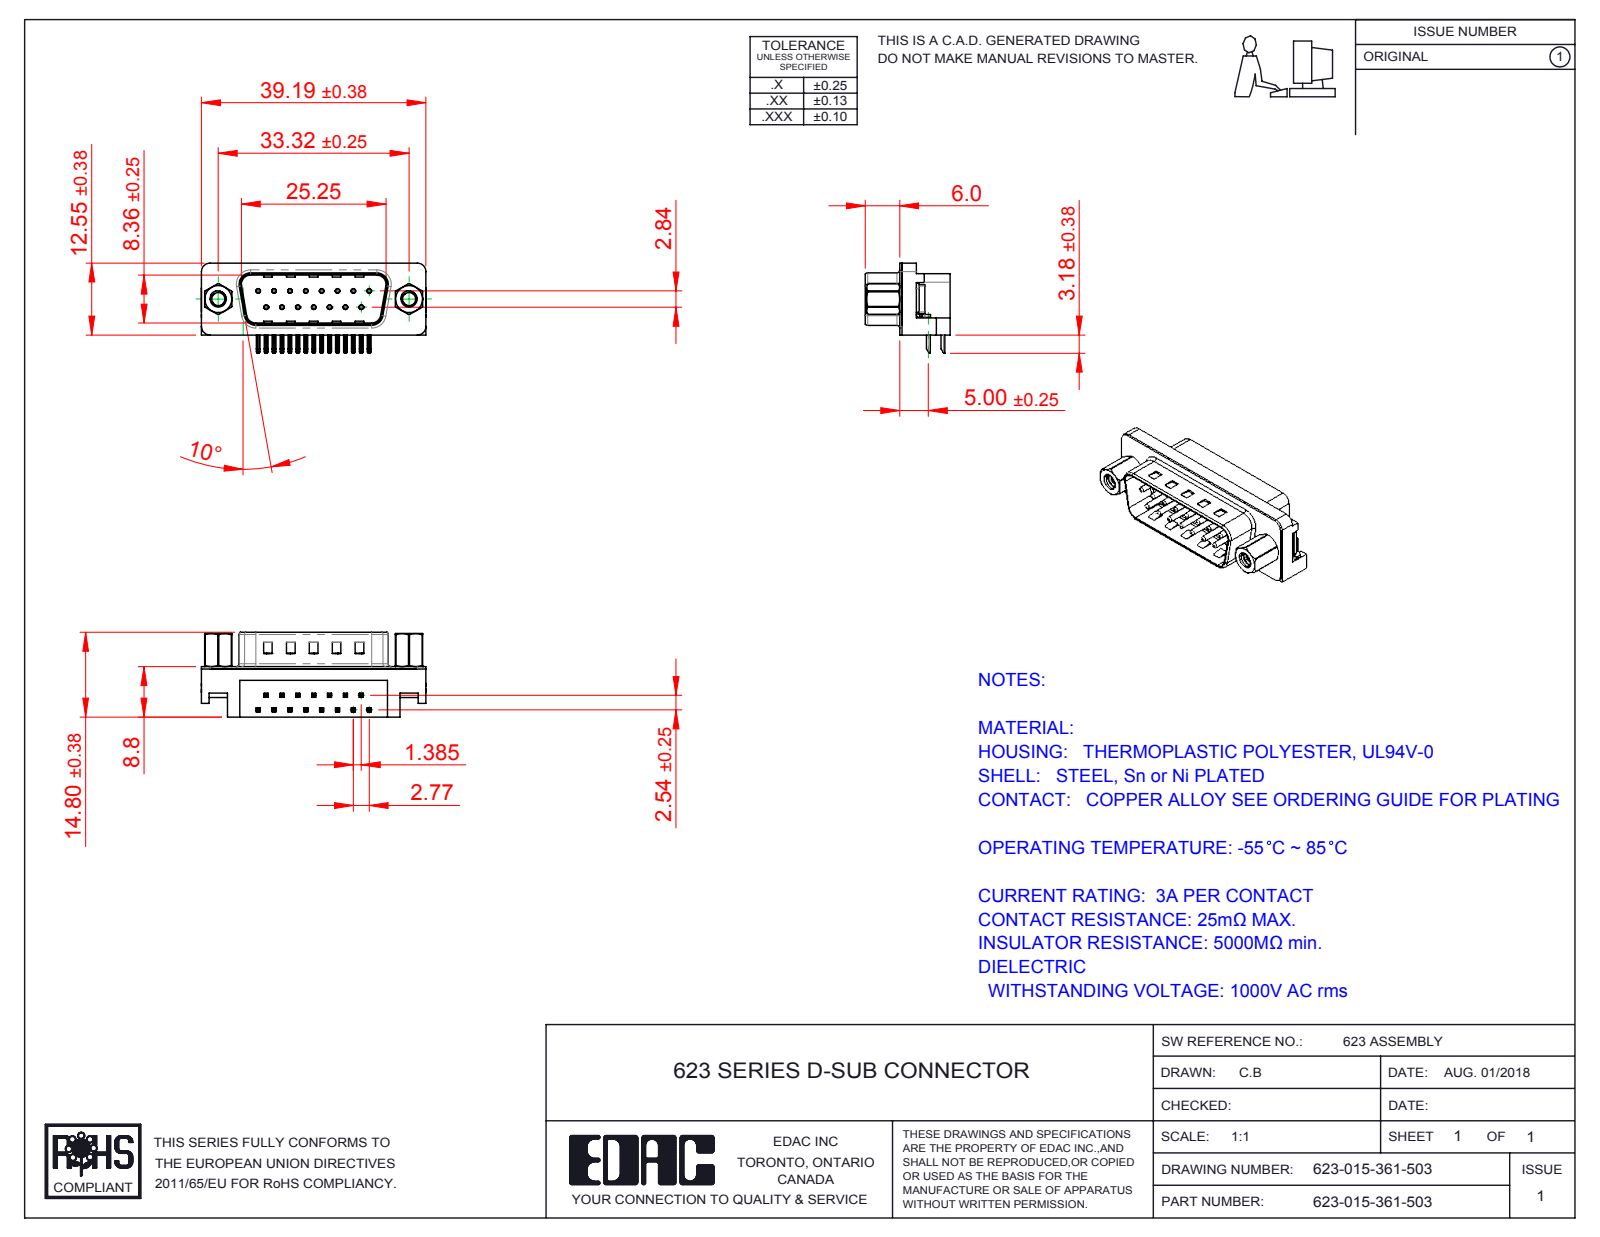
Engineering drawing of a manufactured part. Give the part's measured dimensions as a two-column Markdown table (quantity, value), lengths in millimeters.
| quantity | value |
| --- | --- |
| part name | 623 Shell_15 Socket; 623 Non Board Mount; 623 Contact Bottom; 623 4-40 Hex Standoff 5 (+4 more) |
| STEP written by | SolidWorks 2016 (CONFIG_CONTROL_DESIGN) |
| units | millimeters |
| bodies | 23 solids, 1591 faces (915 planar, 503 cylindrical, 173 other) |
| overall size | 39.22 × 15.73 × 14.8 |
| volume | 3 527 mm³ |
| surface area | 5 355 mm² |
| round holes (diameter × count) | 0.35 × 15, 0.8 × 15, 2.26 × 2, 2.29 × 2, 4 × 2, 4.8 × 2, 5 × 2 |
| round bosses / shafts (diameter × count) | 0.75 × 15, 4.9 × 2, 4.75 × 2, 3.9 × 2, 2.79 × 2 |
| partial cylindrical surfaces (radius × count) | 0.25 × 68, 0.12 × 30, 1 × 16, 0.5 × 9, 1.5 × 6, 0.9 × 4, 1.6 × 4, 2 × 4 |
| main face-to-face distances | 0.4, 8.4, 8.8, 2.1, 1.7, 10.46, 10.86, 8.76, 5.9, 2.9 |
| hole center spacings | 3.16, 2.77, 5.54, 8.31, 11.08, 5.03, 5.04, 7.48 |
